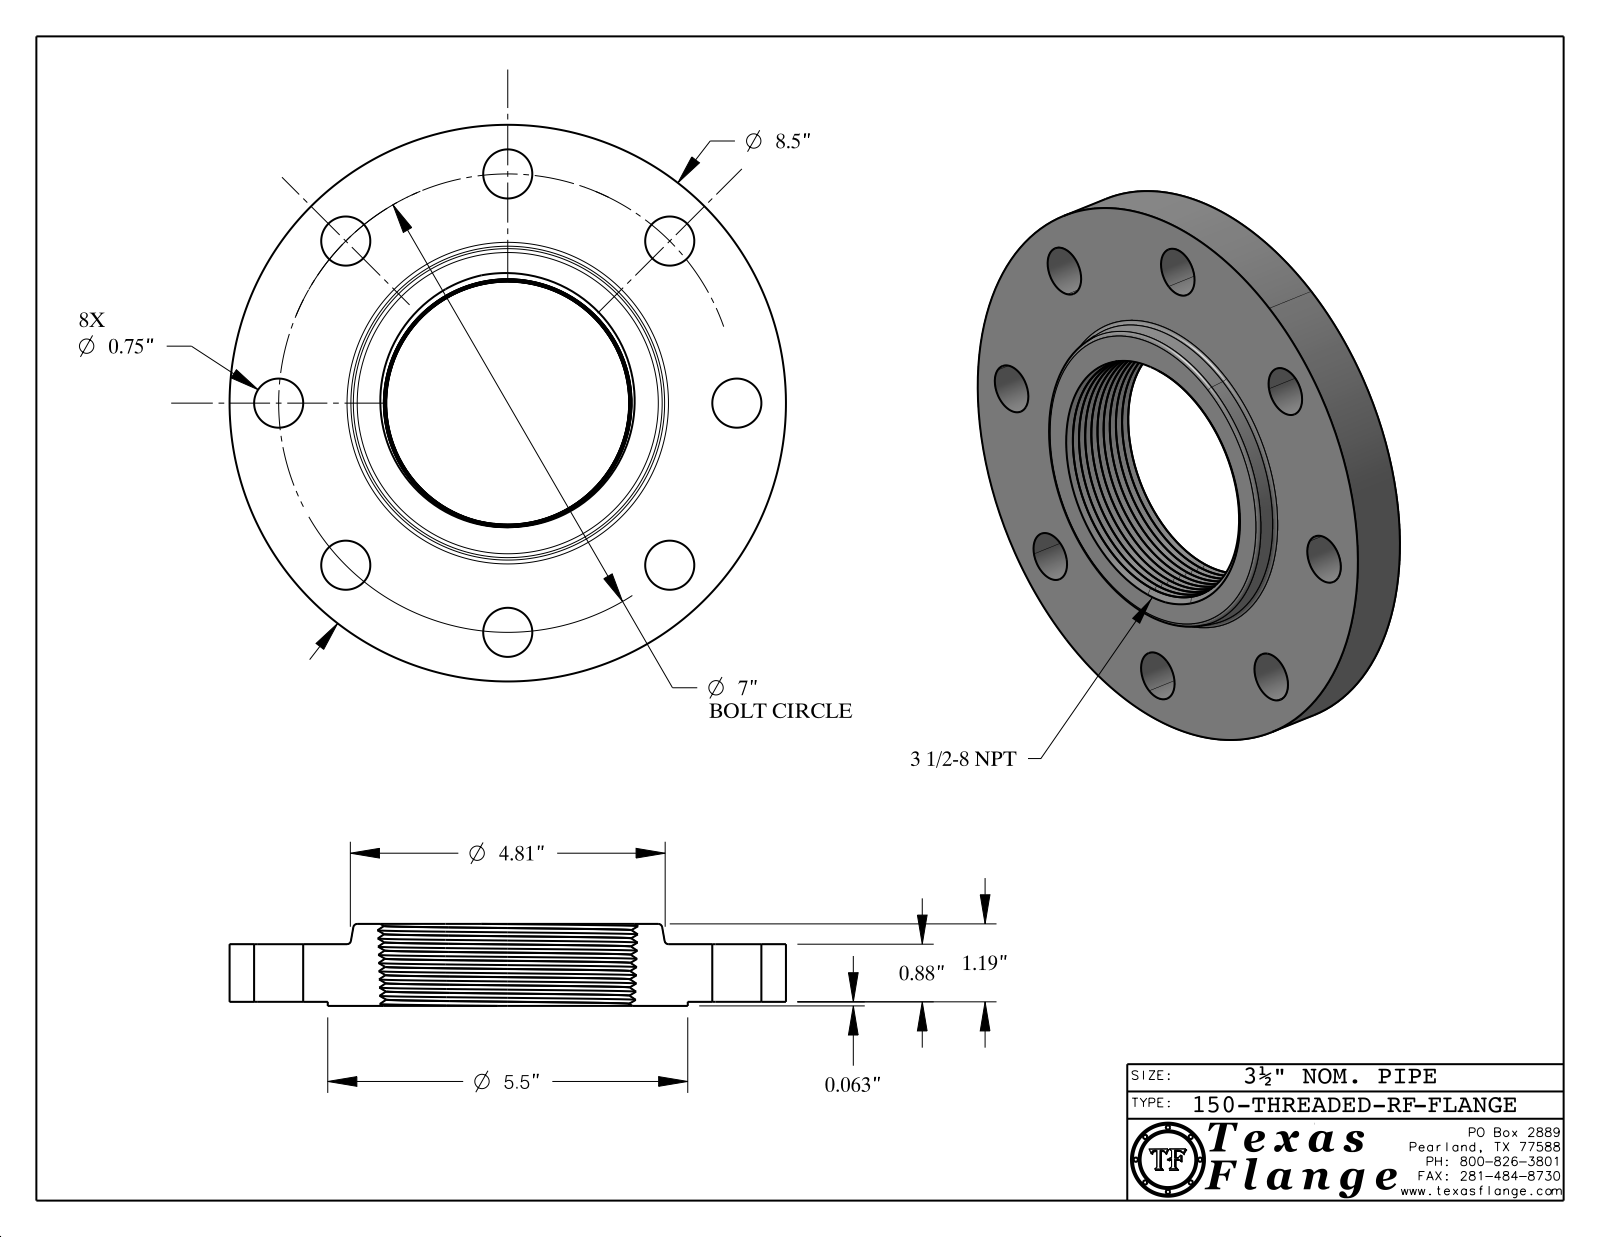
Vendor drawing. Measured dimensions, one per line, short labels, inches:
name: 150-THREADED-RF
written by: CATIA V5 STEP AP214 (AUTOMOTIVE_DESIGN)
unit: in
bodies: 1 solid, 523 faces (369 planar, 40 cylindrical, 114 other)
size: 8.5 × 8.5 × 1.253
volume: 39.26 in³; area: 156.2 in²
holes: 8× ⌀0.75, 1× ⌀0.495
bosses: 8× ⌀0.03, 1× ⌀8.5, 1× ⌀5.5, 1× ⌀0.39
face distances: 0.88, 0.063, 0.943, 1.253, 1.19, 0.31, 0.928, 0.865, 0.015, 0.325
hole spacings: 2.679, 4.95, 6.467, 1.366, 3.889, 5.82, 6.865, 7
